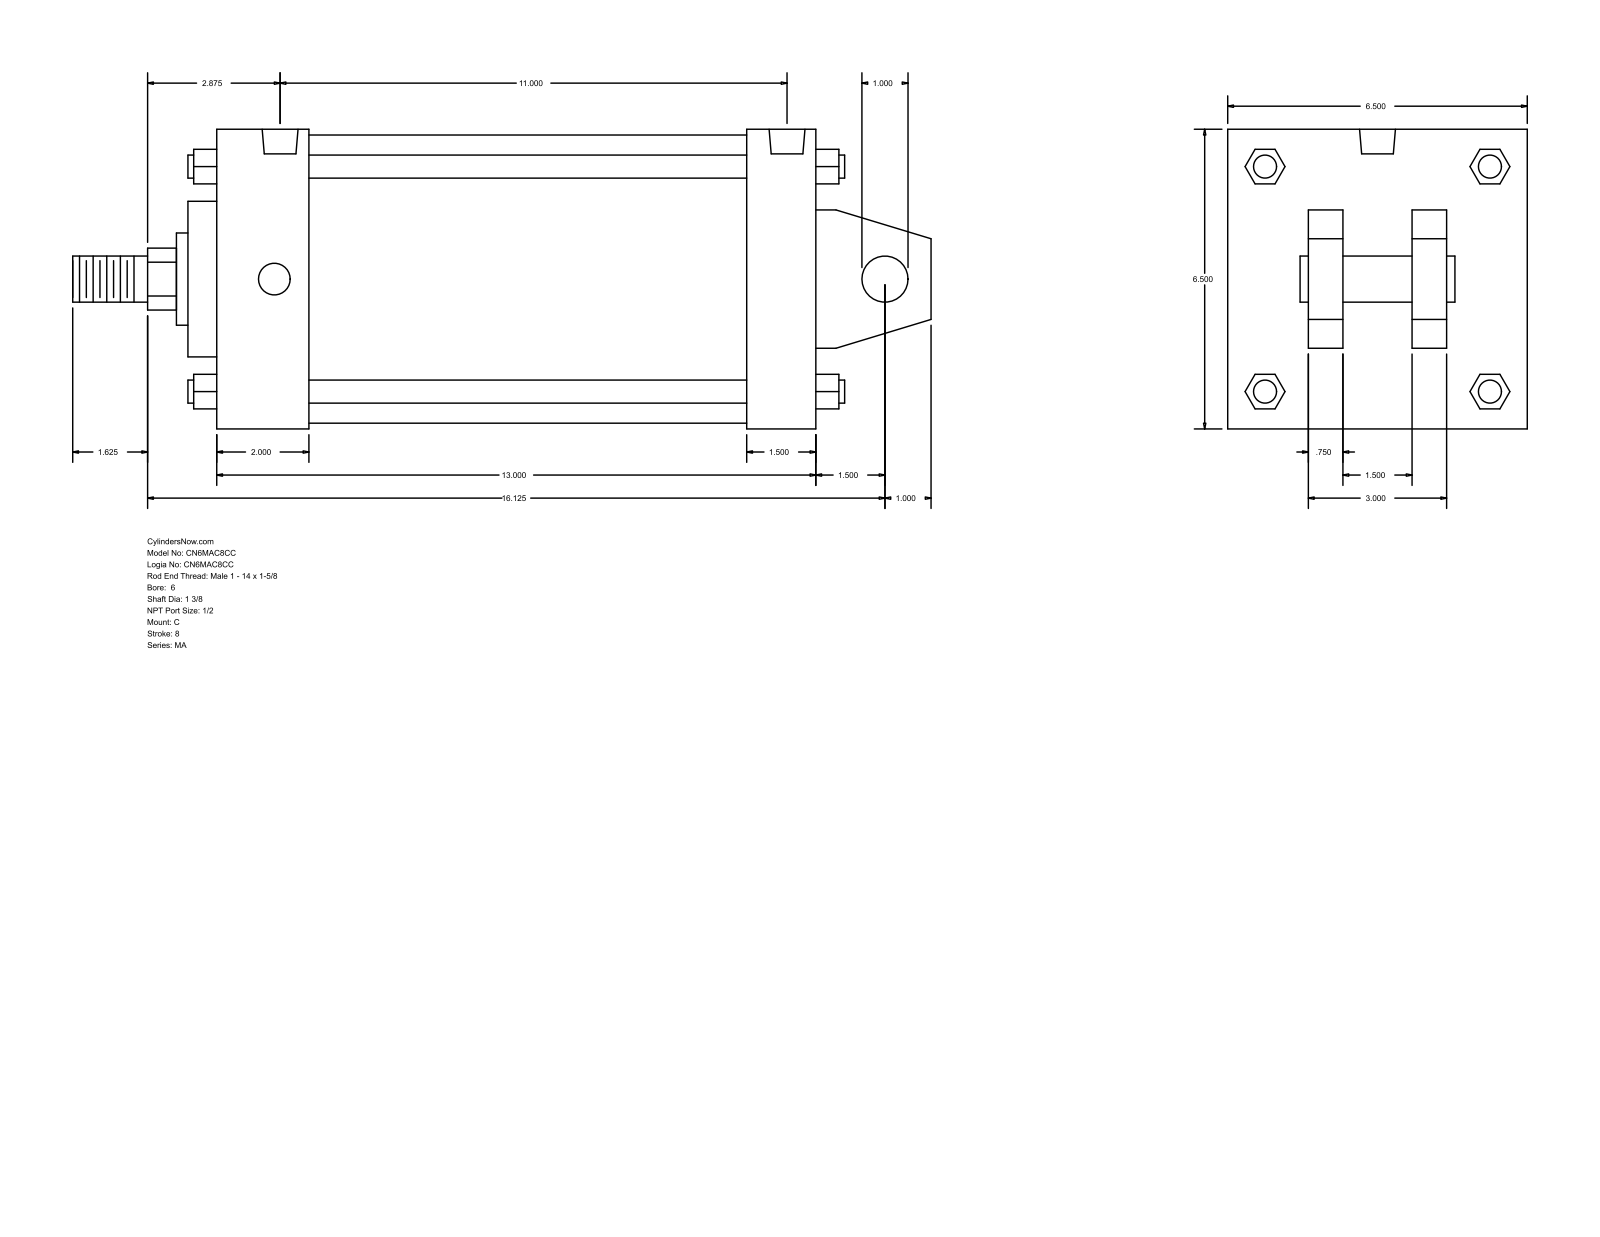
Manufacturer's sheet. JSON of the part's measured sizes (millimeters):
{"part_name": "MA_C__0600_1.375", "step_written_by": "GSSL Pune (CONFIG_CONTROL_DESIGN)", "units": "millimeters", "bodies": {"solids": 0, "faces": 141, "planar": 109, "cylindrical": 32, "other": 0}, "overall_size": [473.07, 165.1, 165.1], "round_holes": [[17.46, 4], [19.77, 2]], "round_bosses_or_shafts": [[12.7, 4], [25.4, 2], [158.75, 1], [85.72, 1], [50.8, 1], [34.92, 1]], "partial_cylinders_radius": [[17.06, 1]], "face_to_face_distances": [165.1, 330.2, 38.1, 19.05, 63.5, 101.6, 50.8, 44.45, 120.65, 292.1], "hole_center_spacings": [279.4, 3.18, 276.22, 282.58]}
